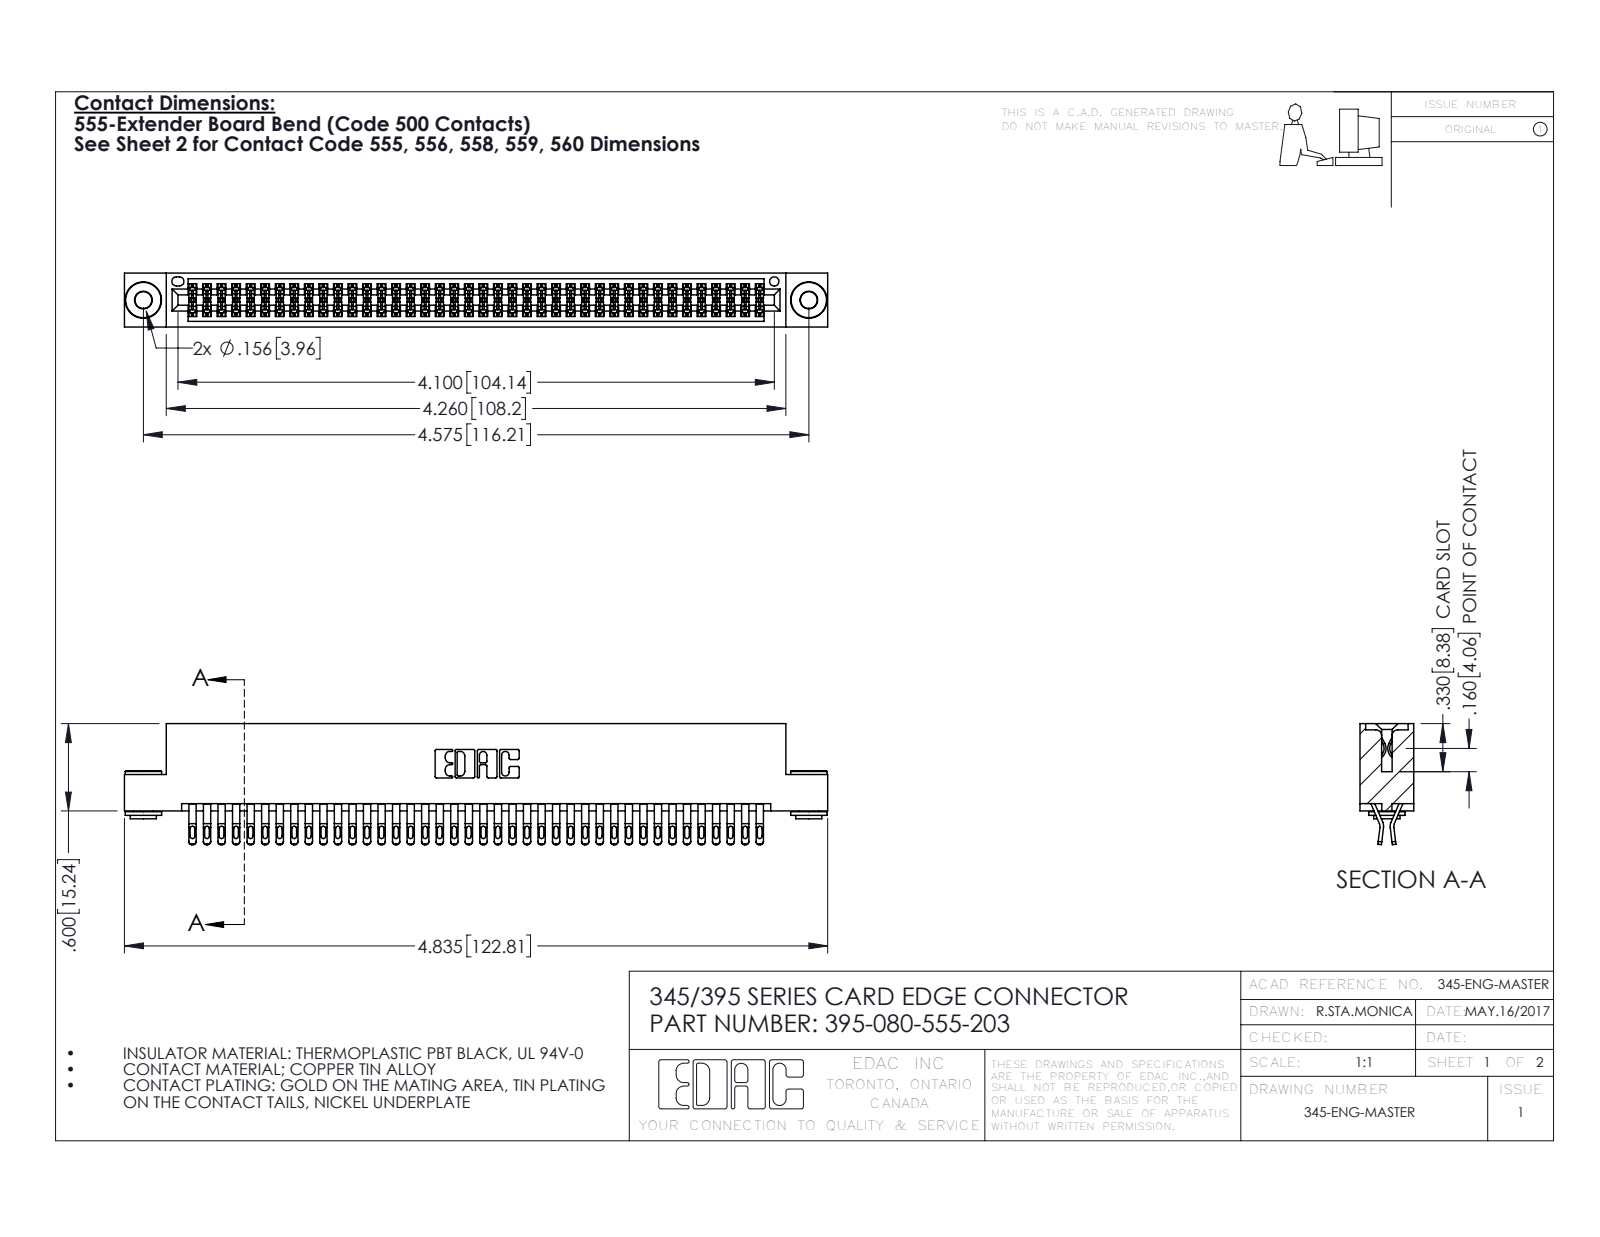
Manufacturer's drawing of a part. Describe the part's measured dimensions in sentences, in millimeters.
The part is named "395-080-555-203; 345-250-002_345-250-002-102; 345-292-001_555 Tail; 345 Part_Flush Mounting Lugs - 0.156 Dia-TH". Its 3-D file was written by "SolidWorks 2016 (CONFIG_CONTROL_DESIGN)". It is 83 solids with 4644 faces: 2570 planar, 2066 cylindrical and 8 other. Overall it measures 122.8 by 21.1 by 9.4 millimeters. Its volume is 12 200 cubic millimeters and its surface area 18 950 square millimeters. Round holes: 2 of diameter 2.9, 2 of diameter 4, 1 of diameter 1.6. Round bosses or shafts: 2 of diameter 6.4, 2 of diameter 4.6, 2 of diameter 3.5. Partial cylindrical surfaces (rounded edges, fillets, slot ends): 200 of radius 0.4, 160 of radius 0.5, 120 of radius 0.2, 22 of radius 0.3, 6 of radius 0.2, 6 of radius 0.8, 3 of radius 0.7, 2 of radius 0.3. The main face-to-face distances are 1.8, 7.6, 5.1, 0.6, 9.4, 2.5, 6.9, 5.7, 4.4, 3.8. The hole center spacings are 6.9, 110.2, 116.2.
